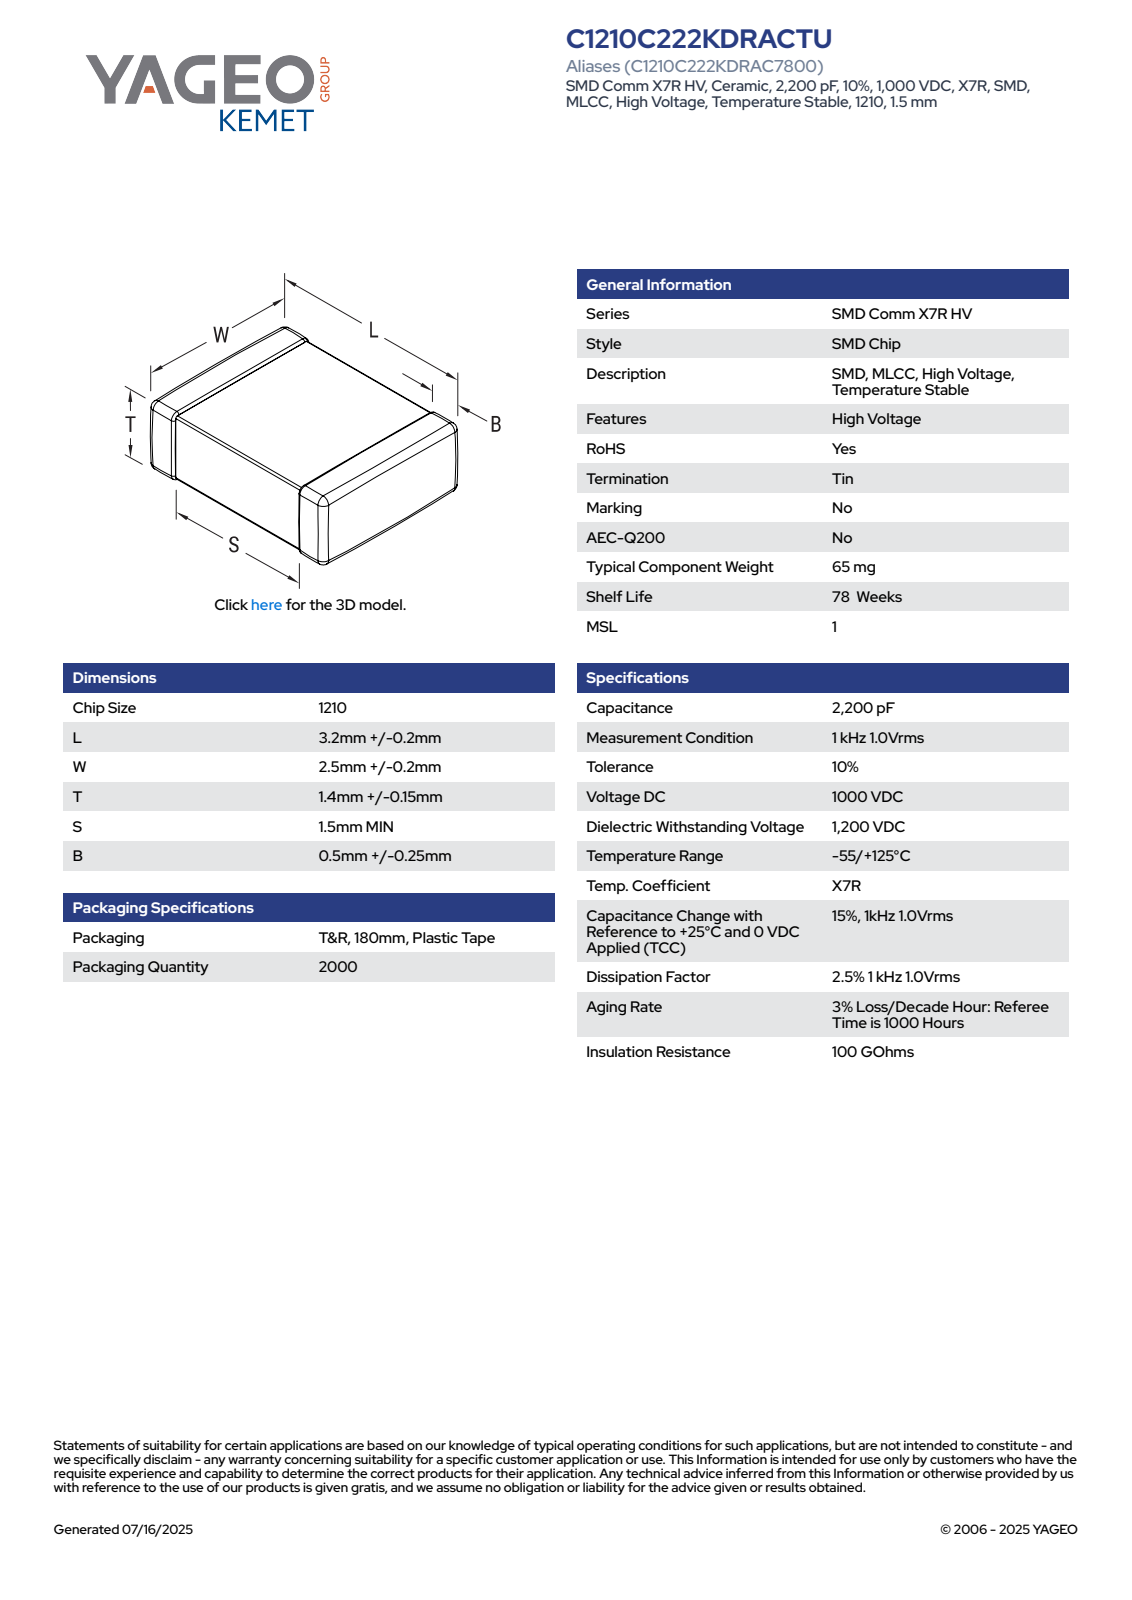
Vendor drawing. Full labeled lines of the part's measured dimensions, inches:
Part name (STEP PRODUCT): CCS_CCSTDNOS_1210_L3.4W2.7T1.55B0.75
STEP written by: SolidWorks 2014 (AUTOMOTIVE_DESIGN)
Units: inches
Bodies: 4 solids, 125 faces (71 planar, 38 cylindrical, 16 other)
Overall size (bounding box): 0.134 × 0.106 × 0.061
Volume: 0.001 in³ · Surface area: 0.057 in²
Main face-to-face distances: 0.059, 0.056, 0.134, 0.104, 0.061, 0.102, 0.106, 0.057, 0.059, 0.052
